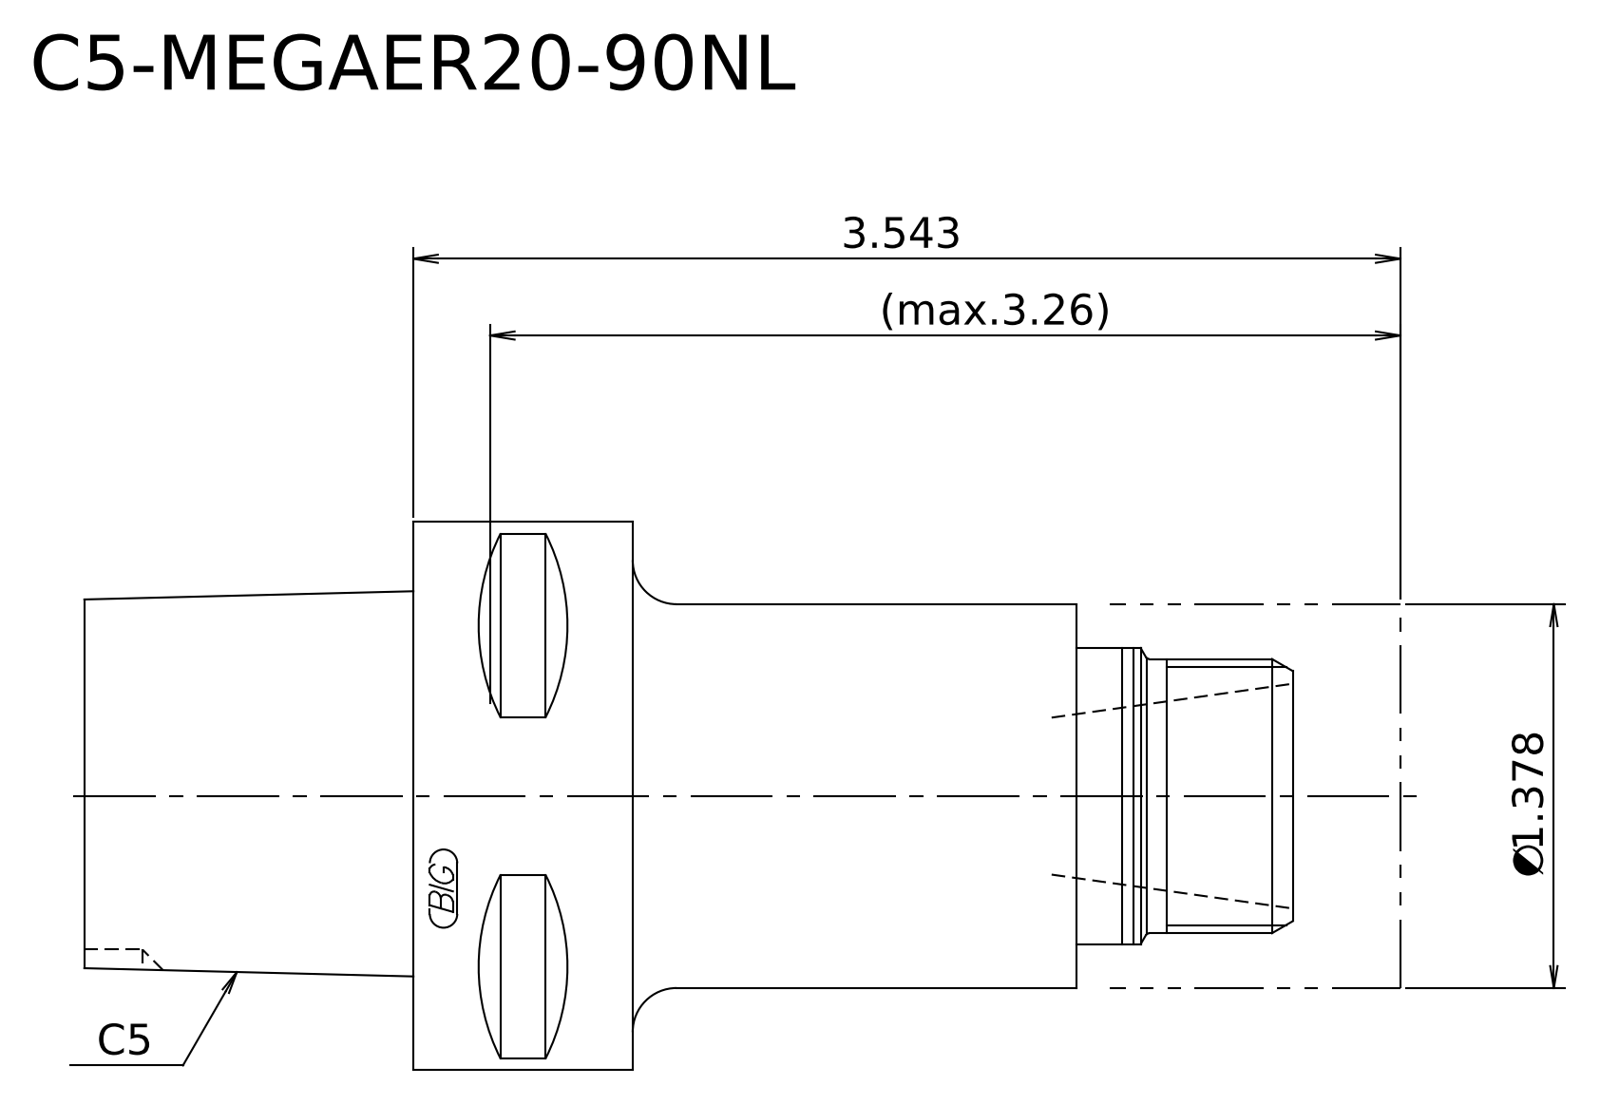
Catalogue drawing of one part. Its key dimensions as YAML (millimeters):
step_written_by: "Kubotek KeyCreator 2011 V10.0.2 (22737) (automotive_design)"
units: millimeters
bodies: {solids: 2, faces: 16, planar: 7, cylindrical: 5, other: 4}
overall_size: [120, 50, 50]
volume: 141968
surface_area: 20768
round_bosses_or_shafts:
  - {diameter: 50, count: 1}
  - {diameter: 35, count: 1}
  - {diameter: 27, count: 1}
  - {diameter: 25, count: 1}
face_to_face_distances: [63.5, 26.5, 90, 120, 93.5, 30, 70, 43.5, 20, 50]
